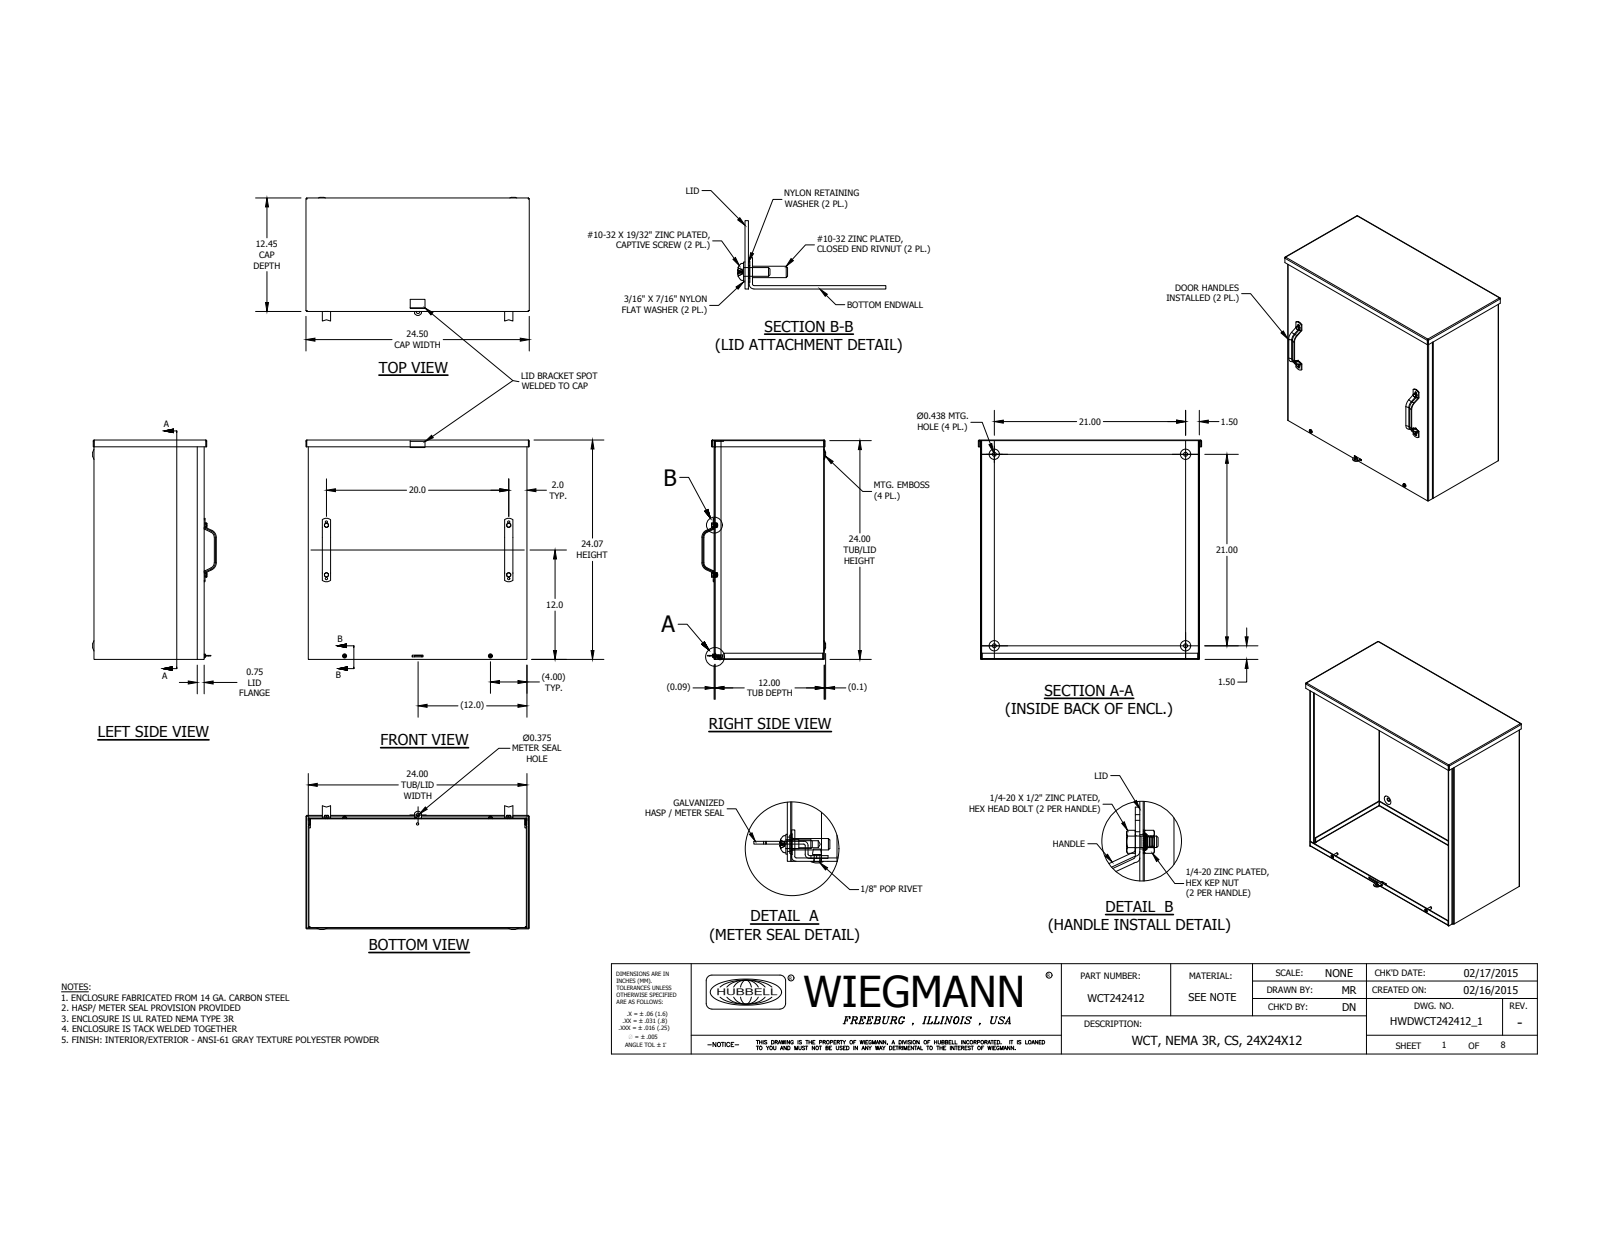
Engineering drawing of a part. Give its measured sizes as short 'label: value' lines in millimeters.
name: WCT242412BKP; WCT2412BTM; WCT2424LID; WCT2412CAP (+8 more)
written by: Autodesk Inventor 2014 (AUTOMOTIVE_DESIGN)
unit: mm
bodies: 29 solids, 1080 faces (528 planar, 313 cylindrical, 239 other)
size: 622.3 × 612.5 × 344.6
volume: 2 984 000 mm³; area: 3 194 000 mm²
holes: 6× ⌀7.94, 4× ⌀4.83, 4× ⌀6.35, 4× ⌀7.33, 4× ⌀8.51, 4× ⌀9.65, 4× ⌀11.11, 2× ⌀3.17, 2× ⌀3.96, 2× ⌀4.78, 2× ⌀4.98, 2× ⌀6.53
bosses: 4× ⌀11.13, 4× ⌀9.52, 4× ⌀8.38, 4× ⌀7.11, 2× ⌀11.51, 2× ⌀11.11, 2× ⌀10.31, 2× ⌀9.47
rounds: 96× R0.51, 19× R0.79, 17× R2.67, 8× R1.27, 8× R2.54, 8× R5.08, 4× R4.93, 4× R17.68
face distances: 1.88, 305.2, 607.72, 609.6, 307.08, 303.32, 605.84, 611.48, 3.94, 603.78
hole spacings: 198.05, 336, 406.4, 470.77, 533.4, 556.95, 619.57, 508
